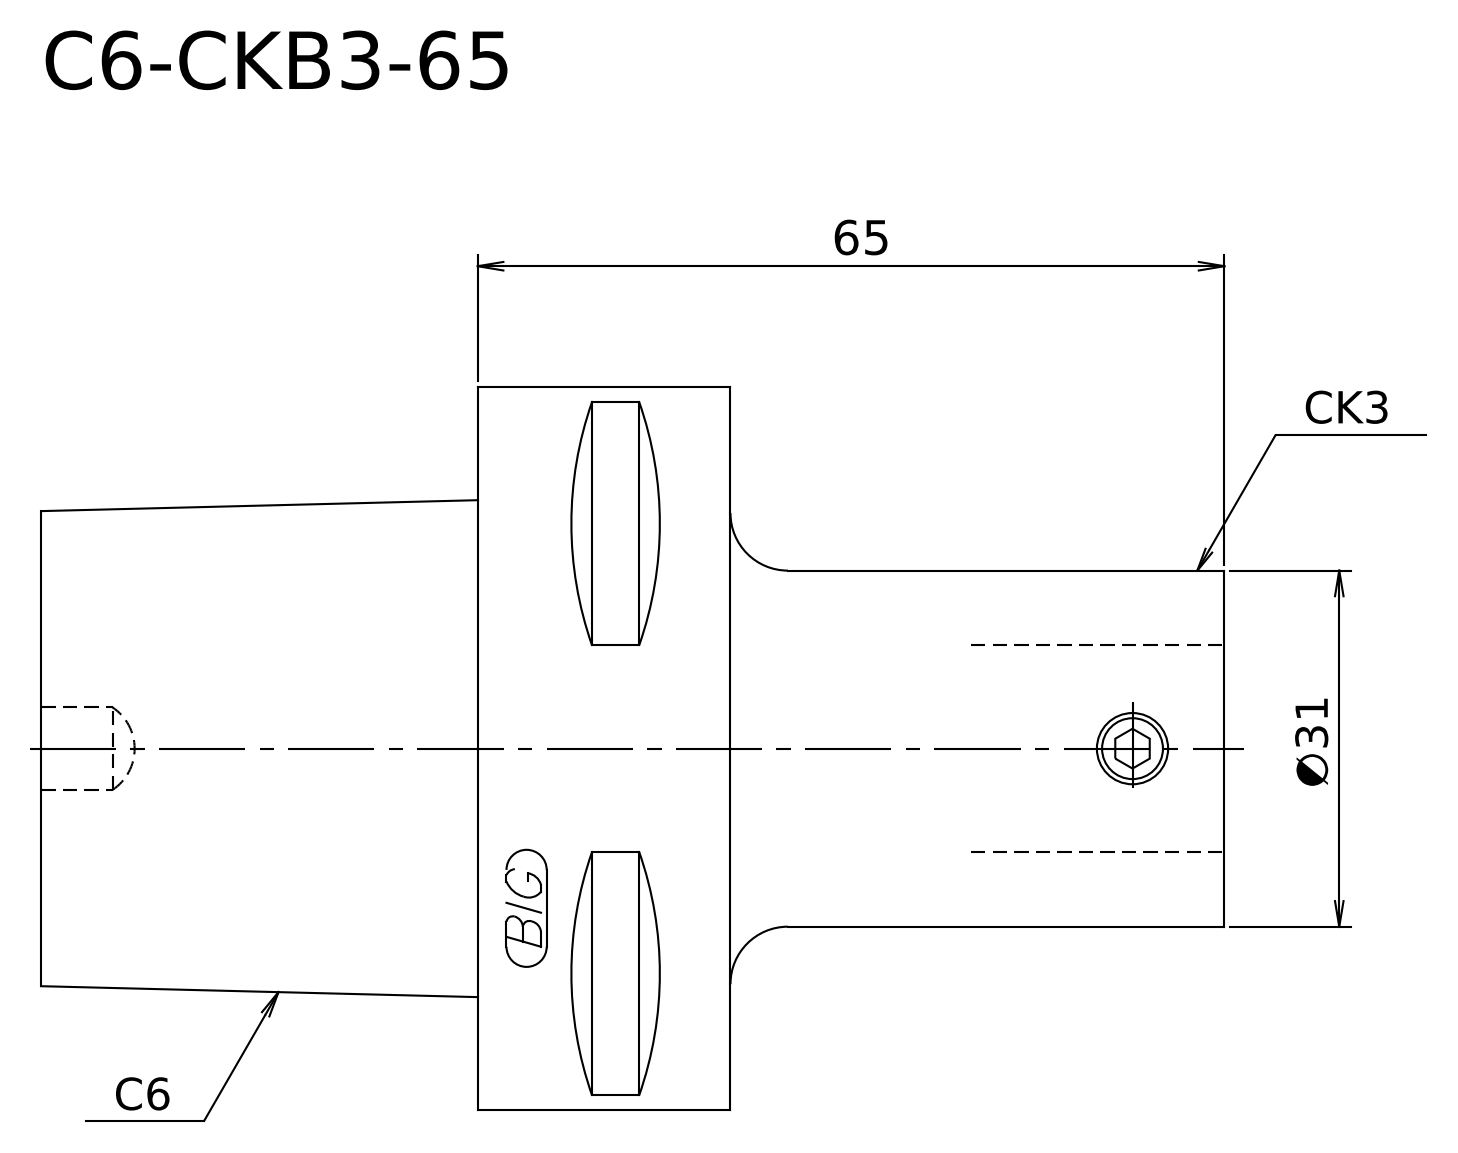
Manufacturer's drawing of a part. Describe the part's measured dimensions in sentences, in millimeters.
Its 3-D file was written by "Kubotek KeyCreator V8.5.1 (14335) (CONFIG_CONTROL_DESIGN)". It is 1 solid with 10 faces: 4 planar, 2 cylindrical and 4 other. Overall it measures 103 by 62.98 by 62.98 millimeters. Its volume is 157 124 cubic millimeters and its surface area 19 549 square millimeters. Round bosses or shafts: 1 of diameter 62.98, 1 of diameter 31. The main face-to-face distances are 22, 60, 38, 43, 65, 103.
